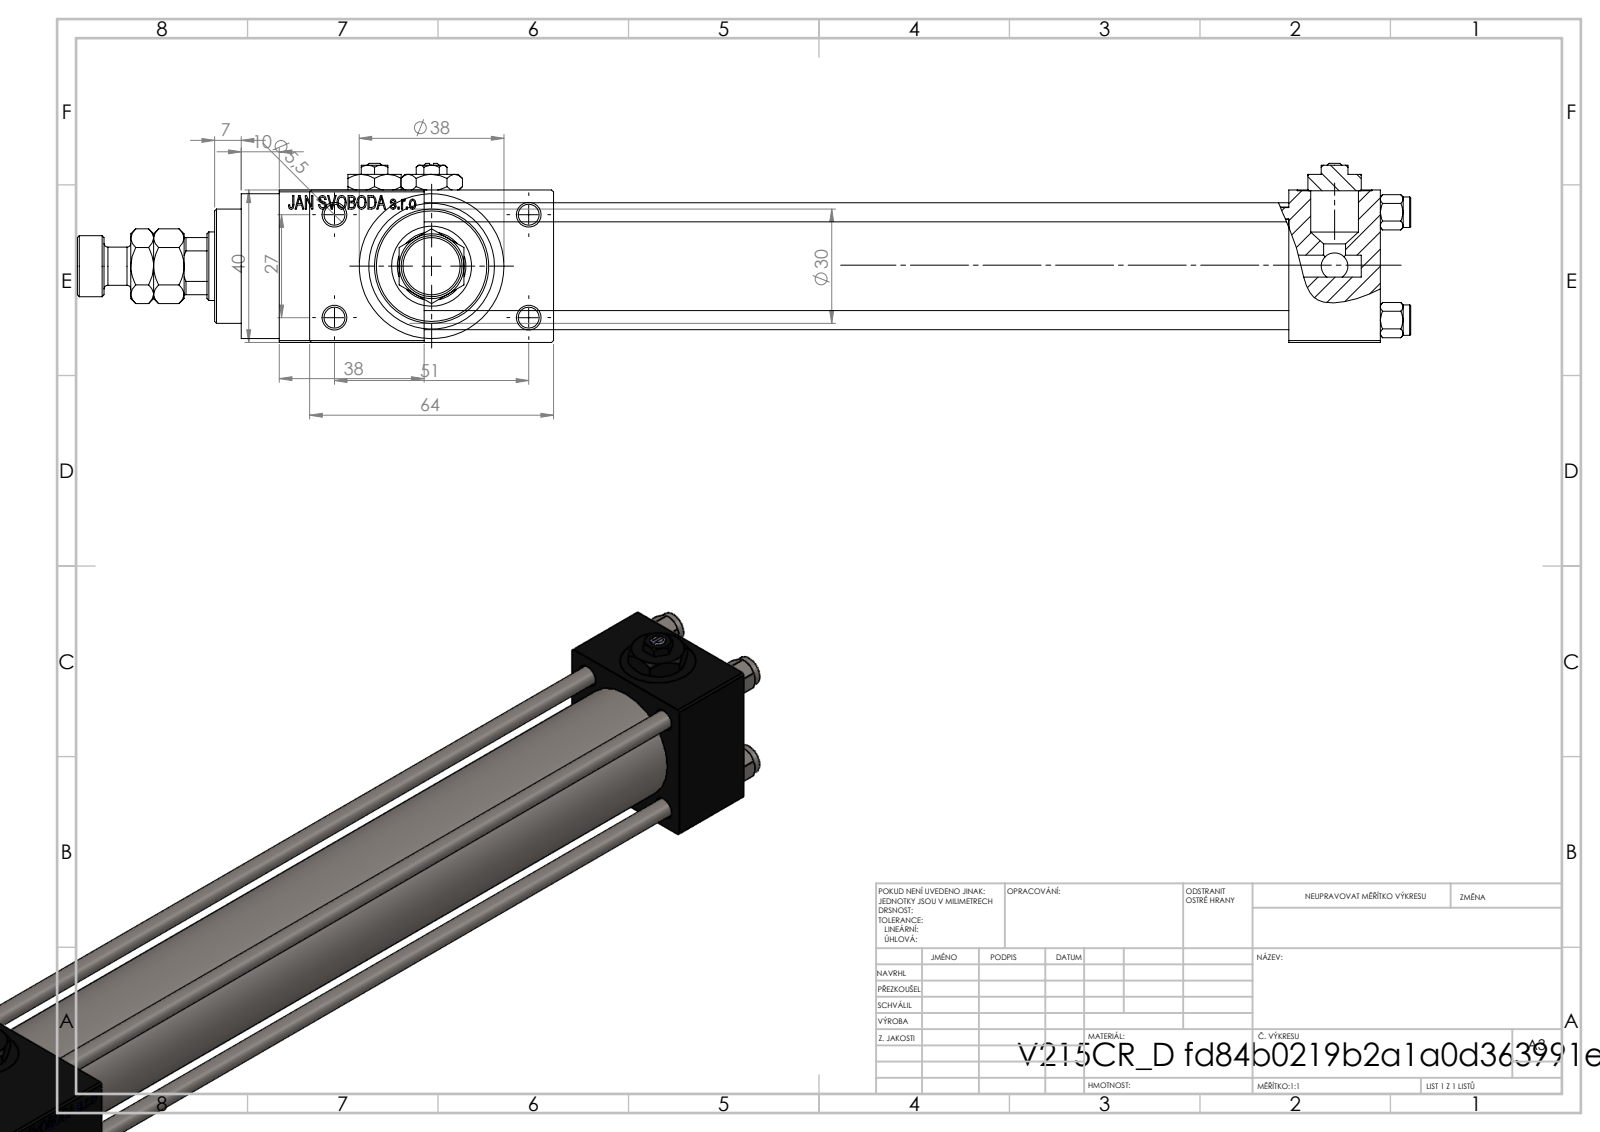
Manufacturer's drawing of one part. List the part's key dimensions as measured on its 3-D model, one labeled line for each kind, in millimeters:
Part name (STEP PRODUCT): V215_VC_A; V215CR_D_Body; Zatka_pro_OIL_PORT; V215CR_D_TYCINKA (+3 more)
STEP written by: SolidWorks 2019 (CONFIG_CONTROL_DESIGN)
Units: millimetres
Bodies: 14 solids, 1252 faces (557 planar, 101 cylindrical, 594 other)
Overall size (bounding box): 350 × 64 × 47
Volume: 290 966 mm³ · Surface area: 121 496 mm²
Round holes (diameter × count): ⌀20 ×5, ⌀5 ×4, ⌀5.5 ×4, ⌀13.16 ×4, ⌀7 ×3, ⌀8.5 ×1, ⌀18 ×1, ⌀21 ×1, ⌀25 ×1, ⌀30 ×1
Round bosses / shafts (diameter × count): ⌀8 ×4, ⌀38 ×1, ⌀31 ×1, ⌀16 ×1, ⌀10 ×1
Partial cylindrical surfaces — rounded edges, fillets, slot ends (radius × count): R8.5 ×1
Main face-to-face distances: 40, 12, 227, 24, 251, 52, 38, 265, 289, 64
Hole centre spacings: 11.37, 20.01, 28.3, 28.85, 29.89, 39.66, 48.34, 27
